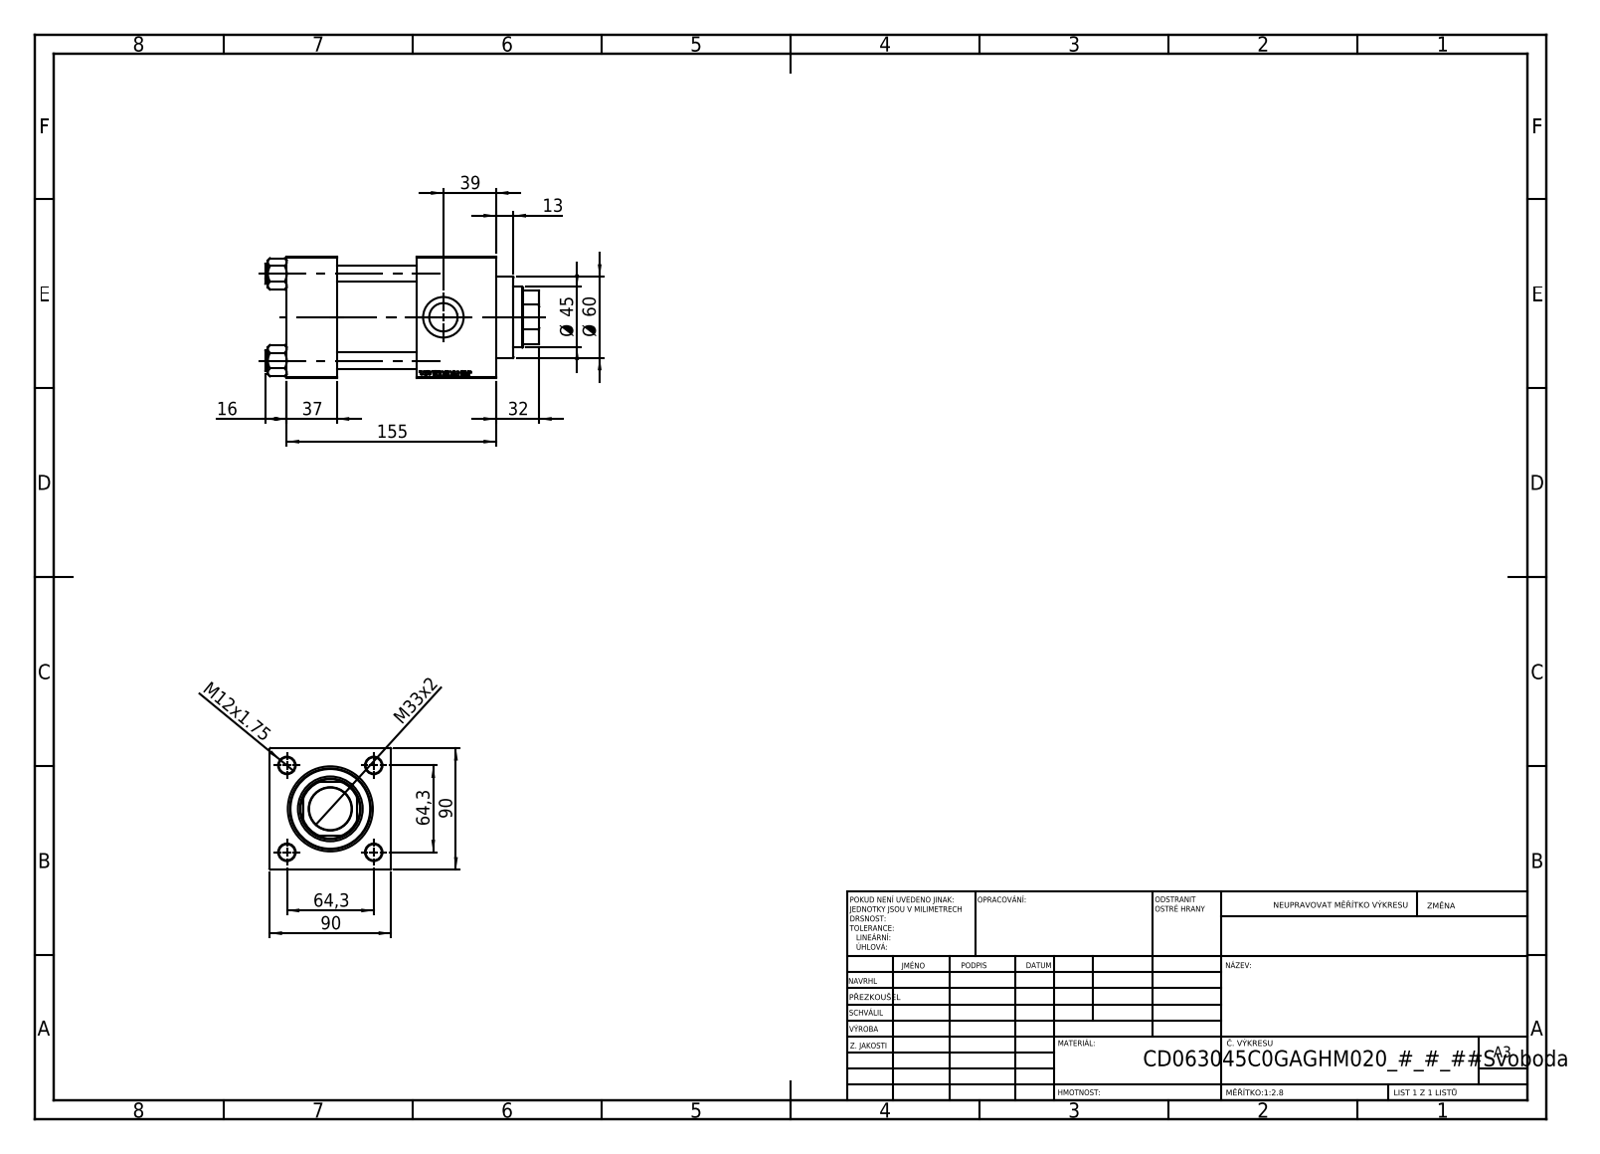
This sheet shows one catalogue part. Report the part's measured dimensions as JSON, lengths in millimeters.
{"part_name": "NUT_M5_V215CD_C; V215CD_VC_C; V215CD_Body_C; V215CD_VCP_C (+1 more)", "step_written_by": "SolidWorks 2019 (CONFIG_CONTROL_DESIGN)", "units": "millimeters", "bodies": {"solids": 11, "faces": 1146, "planar": 525, "cylindrical": 85, "other": 536}, "overall_size": [203, 90, 90], "volume_mm3": 997842, "surface_area_mm2": 189935, "round_holes": [[12, 4], [7, 2], [20.96, 2], [30, 2], [31.5, 1], [45, 1], [48, 1], [50, 1], [60, 1], [63, 1]], "round_bosses_or_shafts": [[15, 4], [69, 1]], "partial_cylinders_radius": [[22, 1]], "face_to_face_distances": [90, 59, 37, 96, 155, 118, 126.3, 89.3, 30.3, 28.7], "hole_center_spacings": [45.47, 64.3, 90.93]}
